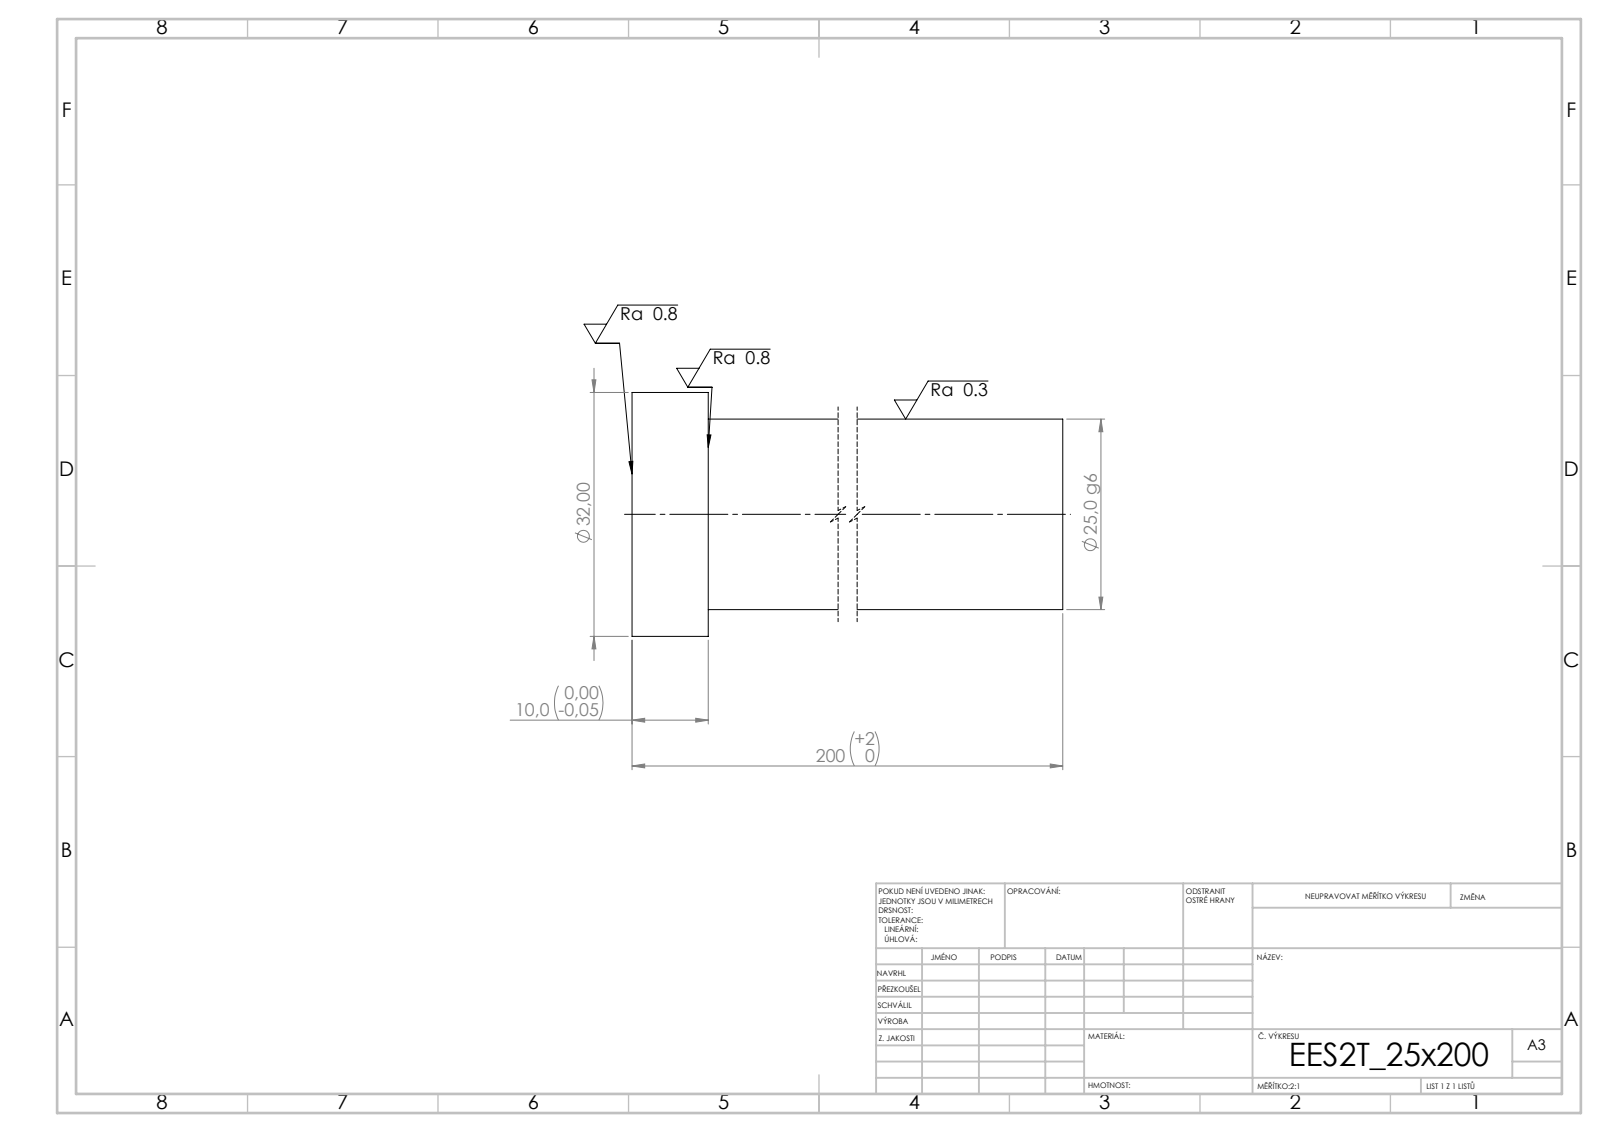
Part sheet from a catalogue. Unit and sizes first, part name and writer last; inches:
Units: inches
Overall size (bounding box): 7.874 × 1.26 × 1.26
Round bosses / shafts (diameter × count): ⌀1.26 ×1, ⌀0.984 ×1
Main face-to-face distances: 7.874, 0.394, 7.48
Volume: 6.182 in³ · Surface area: 27.18 in²
Bodies: 1 solid, 7 faces (3 planar, 4 cylindrical, 0 other)
STEP written by: SolidWorks 2019 (CONFIG_CONTROL_DESIGN)
